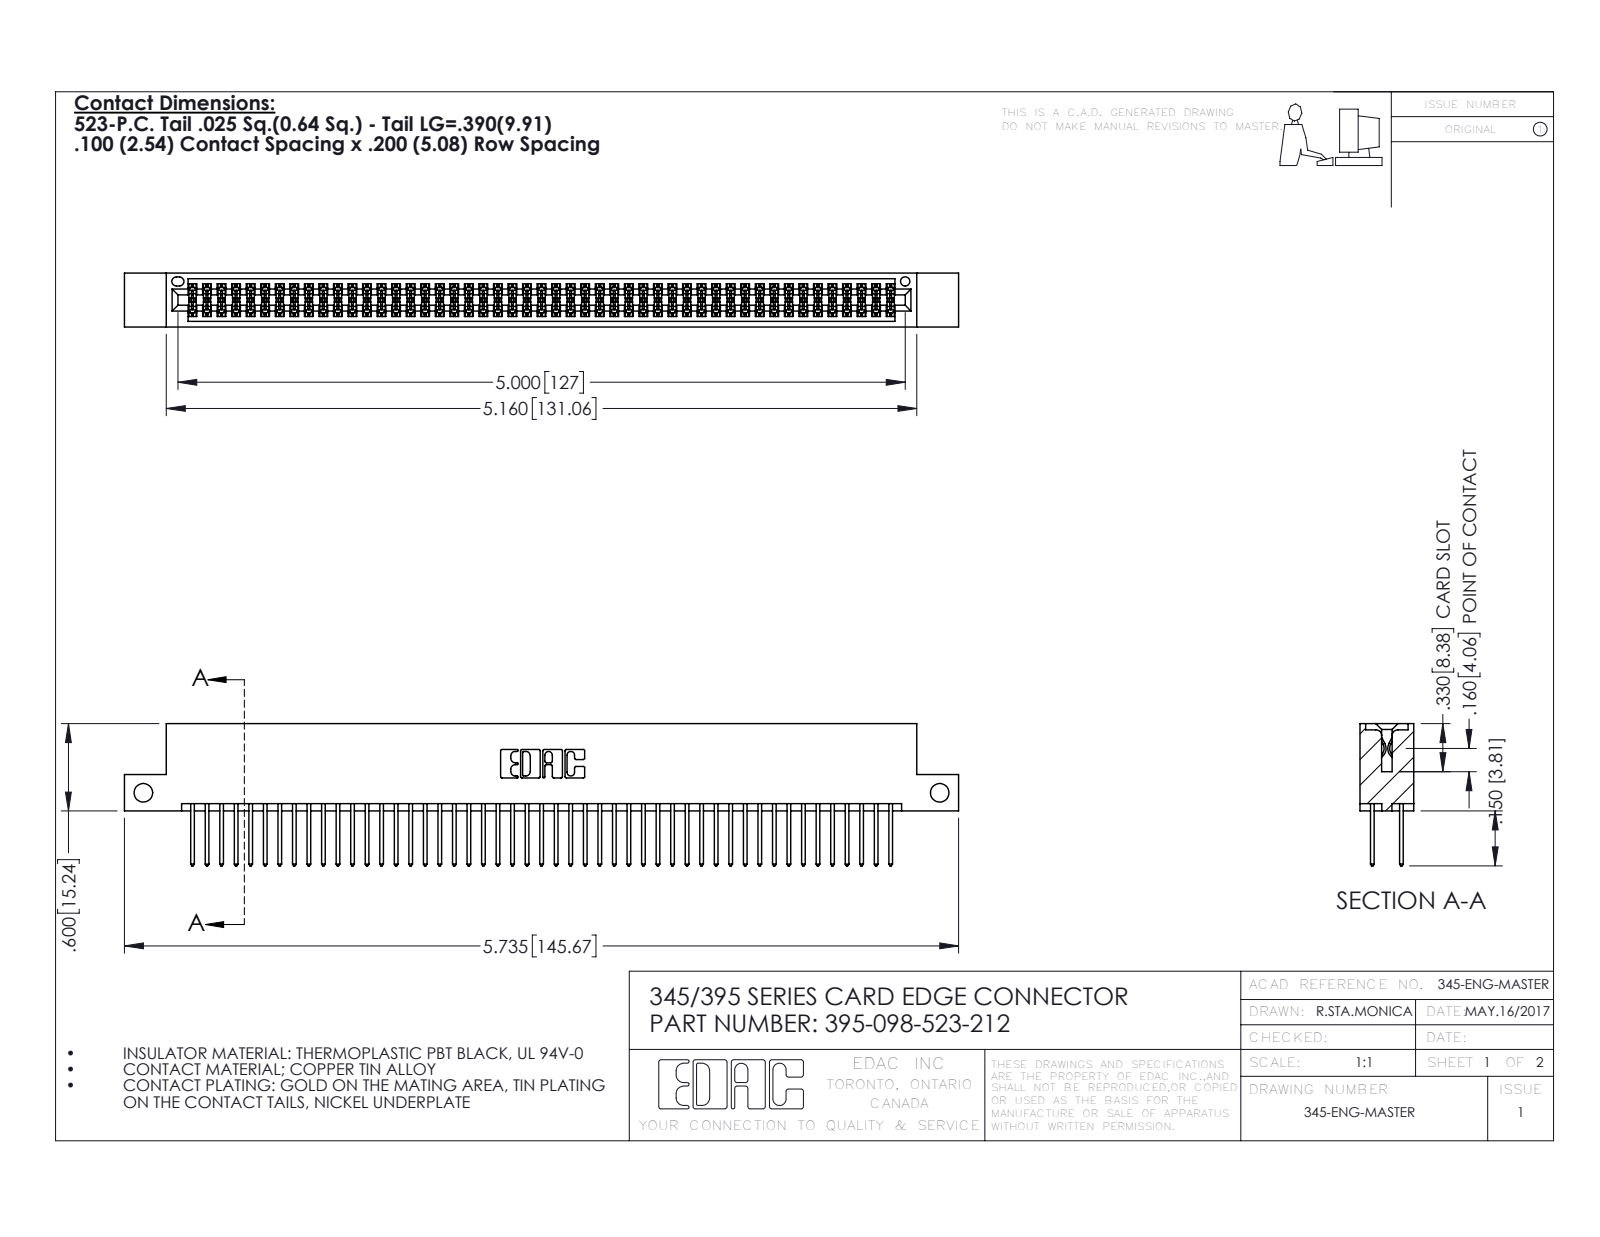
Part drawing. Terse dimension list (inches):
name: 345 Part_Flush Mounting Lugs - Side Mount; 345-292-001_345-293-123; 395-098-523-212
written by: SolidWorks 2016 (CONFIG_CONTROL_DESIGN)
unit: in
bodies: 99 solids, 5026 faces (3314 planar, 1712 cylindrical, 0 other)
size: 5.735 × 0.977 × 0.37
volume: 0.874 in³; area: 34.23 in²
holes: 2× ⌀0.128, 1× ⌀0.064
rounds: 147× R0.006, 98× R0.01, 22× R0.01, 6× R0.007, 6× R0.031, 3× R0.026, 2× R0.014, 2× R0.019
face distances: 0.298, 0.072, 0.2, 0.098, 0.272, 0.025, 0.37, 0.225, 0.175, 0.149
hole spacings: 5.475
